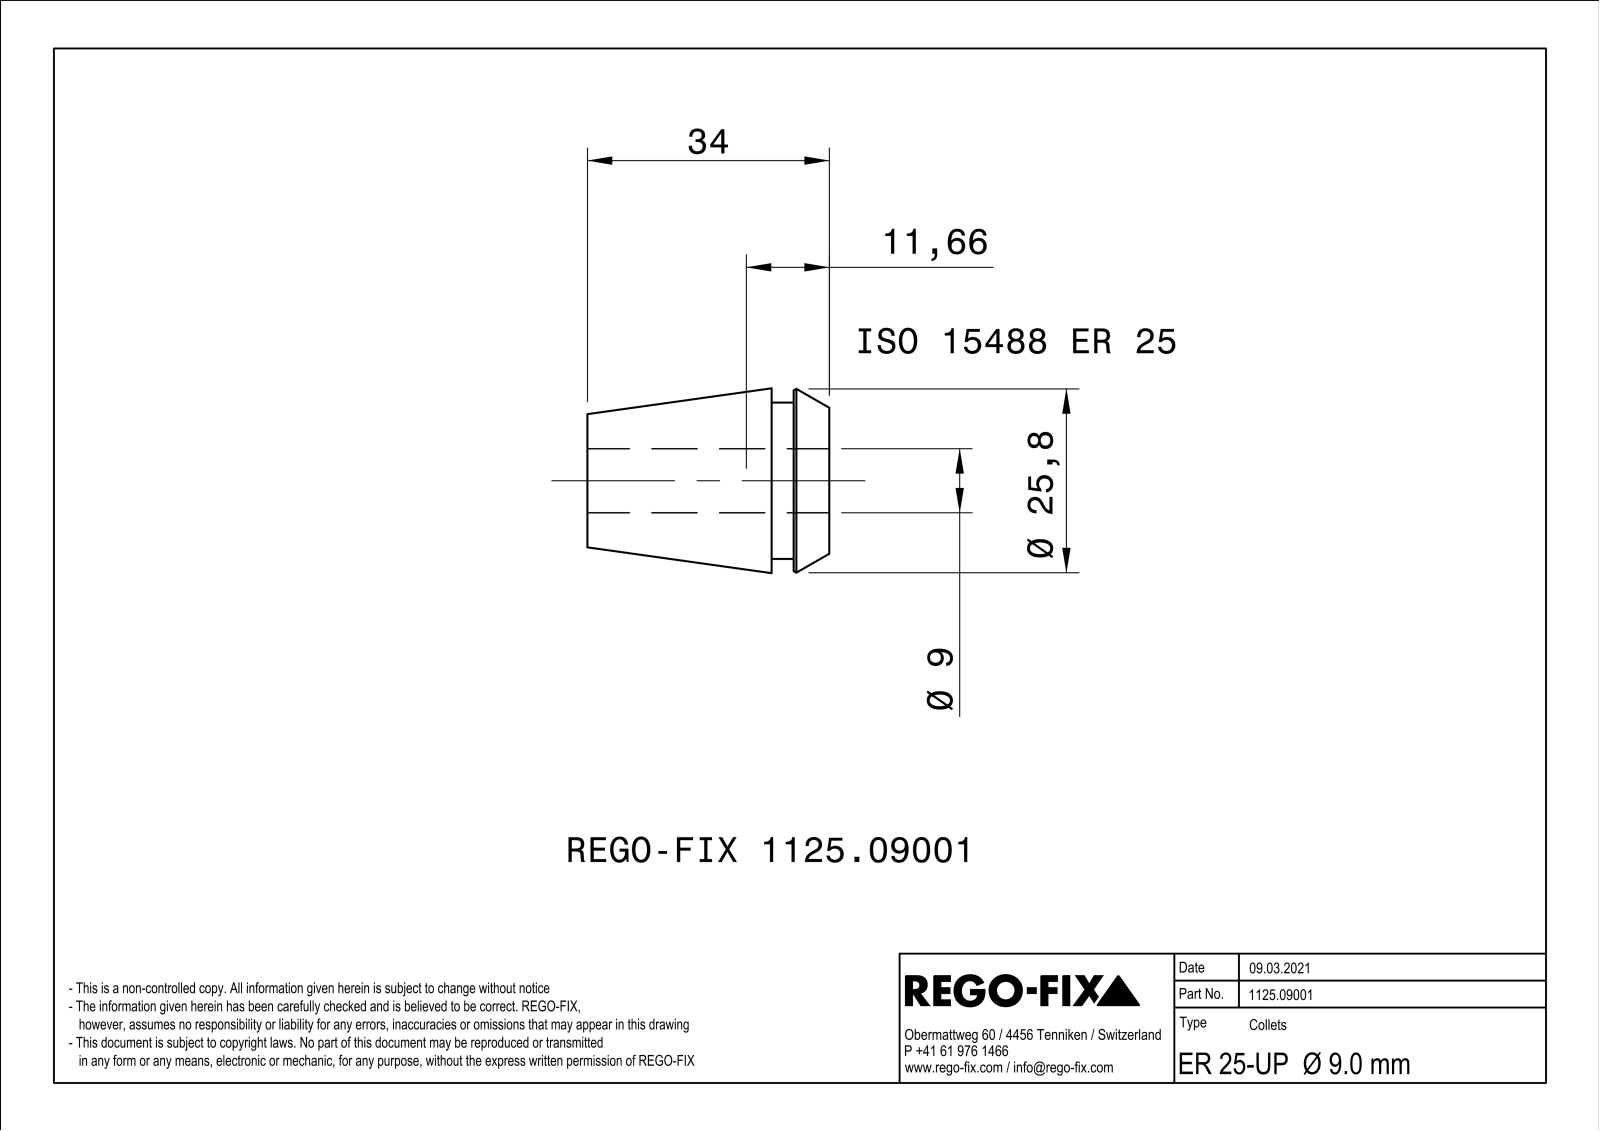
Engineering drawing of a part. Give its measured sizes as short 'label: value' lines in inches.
name: NOCUT
written by: SIEMENS PLM Software Solid Edge ST10 (AUTOMOTIVE_DESIGN)
unit: in
bodies: 1 solid, 177 faces (72 planar, 25 cylindrical, 80 other)
size: 1.339 × 1.023 × 1.023
volume: 0.54 in³; area: 15.21 in²
holes: 1× ⌀0.354
bosses: 1× ⌀0.866
rounds: 8× R0.016
face distances: 0.031, 1.339, 0.319, 1.02, 0.197, 0.122, 1.142
